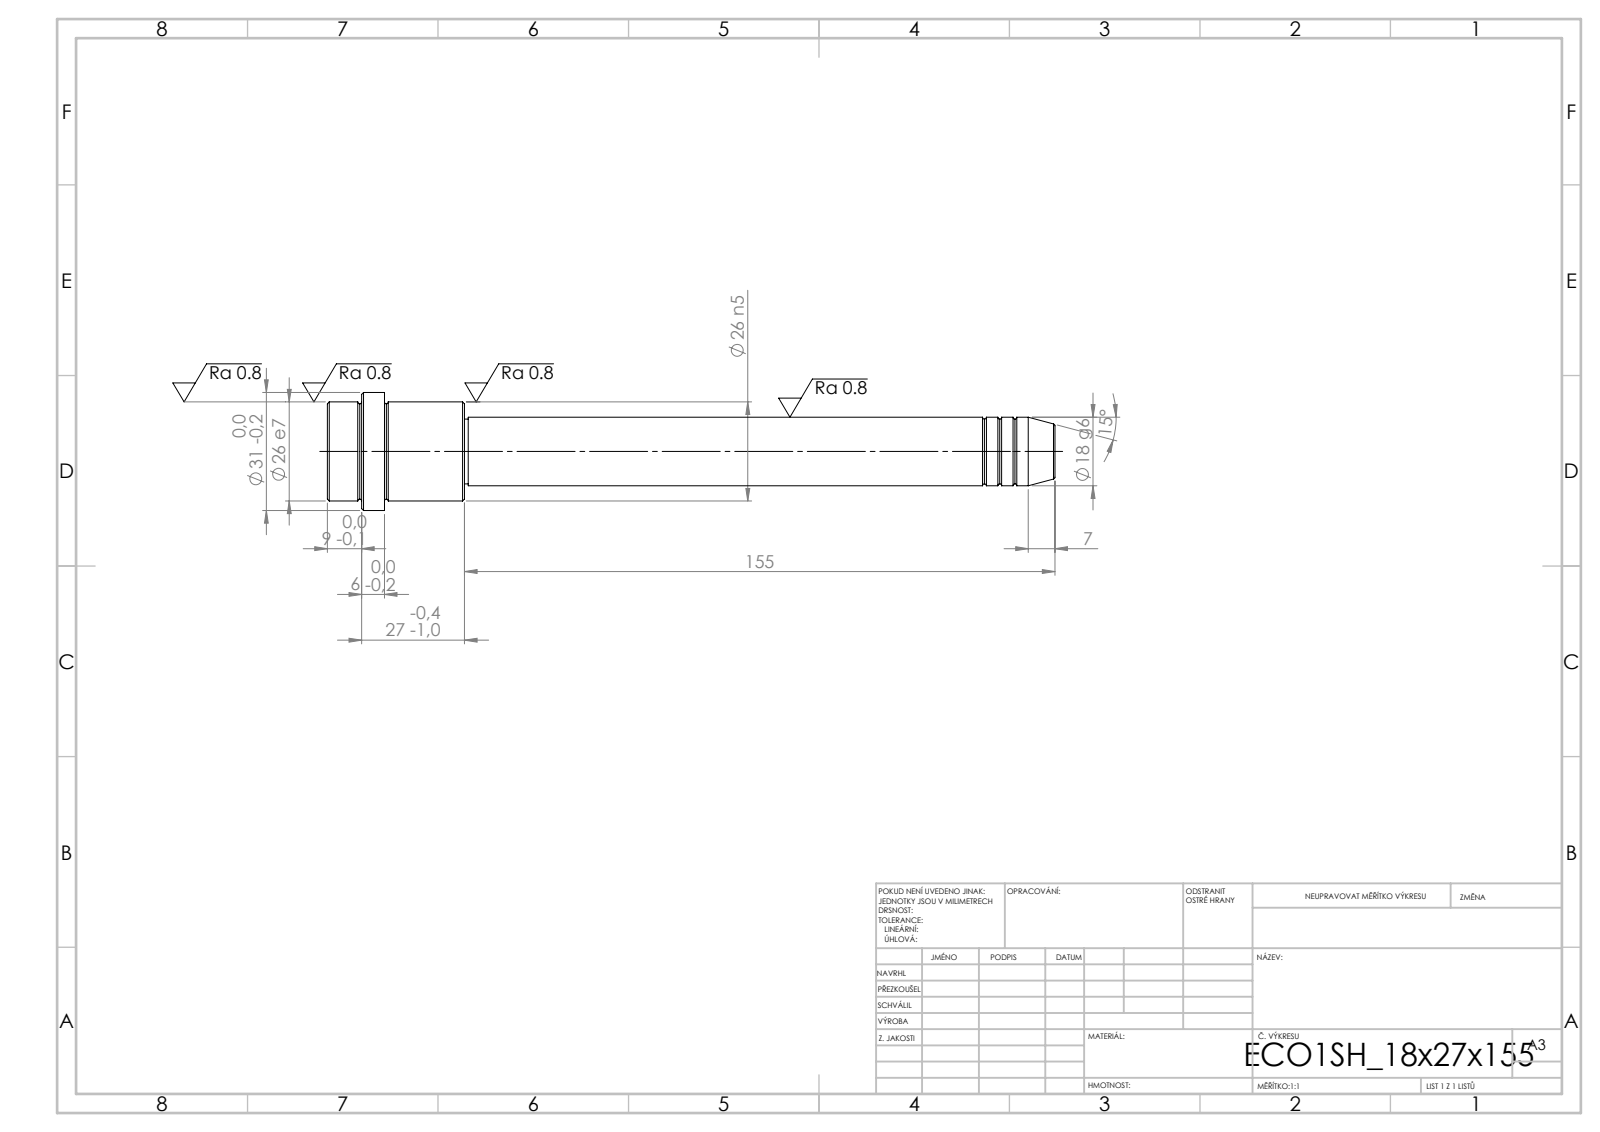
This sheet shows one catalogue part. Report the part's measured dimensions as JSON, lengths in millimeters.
{"step_written_by": "SolidWorks 2019 (CONFIG_CONTROL_DESIGN)", "units": "millimeters", "bodies": {"solids": 1, "faces": 52, "planar": 6, "cylindrical": 16, "other": 30}, "overall_size": [191, 31, 31], "volume_mm3": 59365, "surface_area_mm2": 13329, "round_bosses_or_shafts": [[31, 1], [26, 1], [18, 1], [17, 1]], "face_to_face_distances": [36, 21, 15, 27, 6, 9, 155, 176, 182, 191]}
